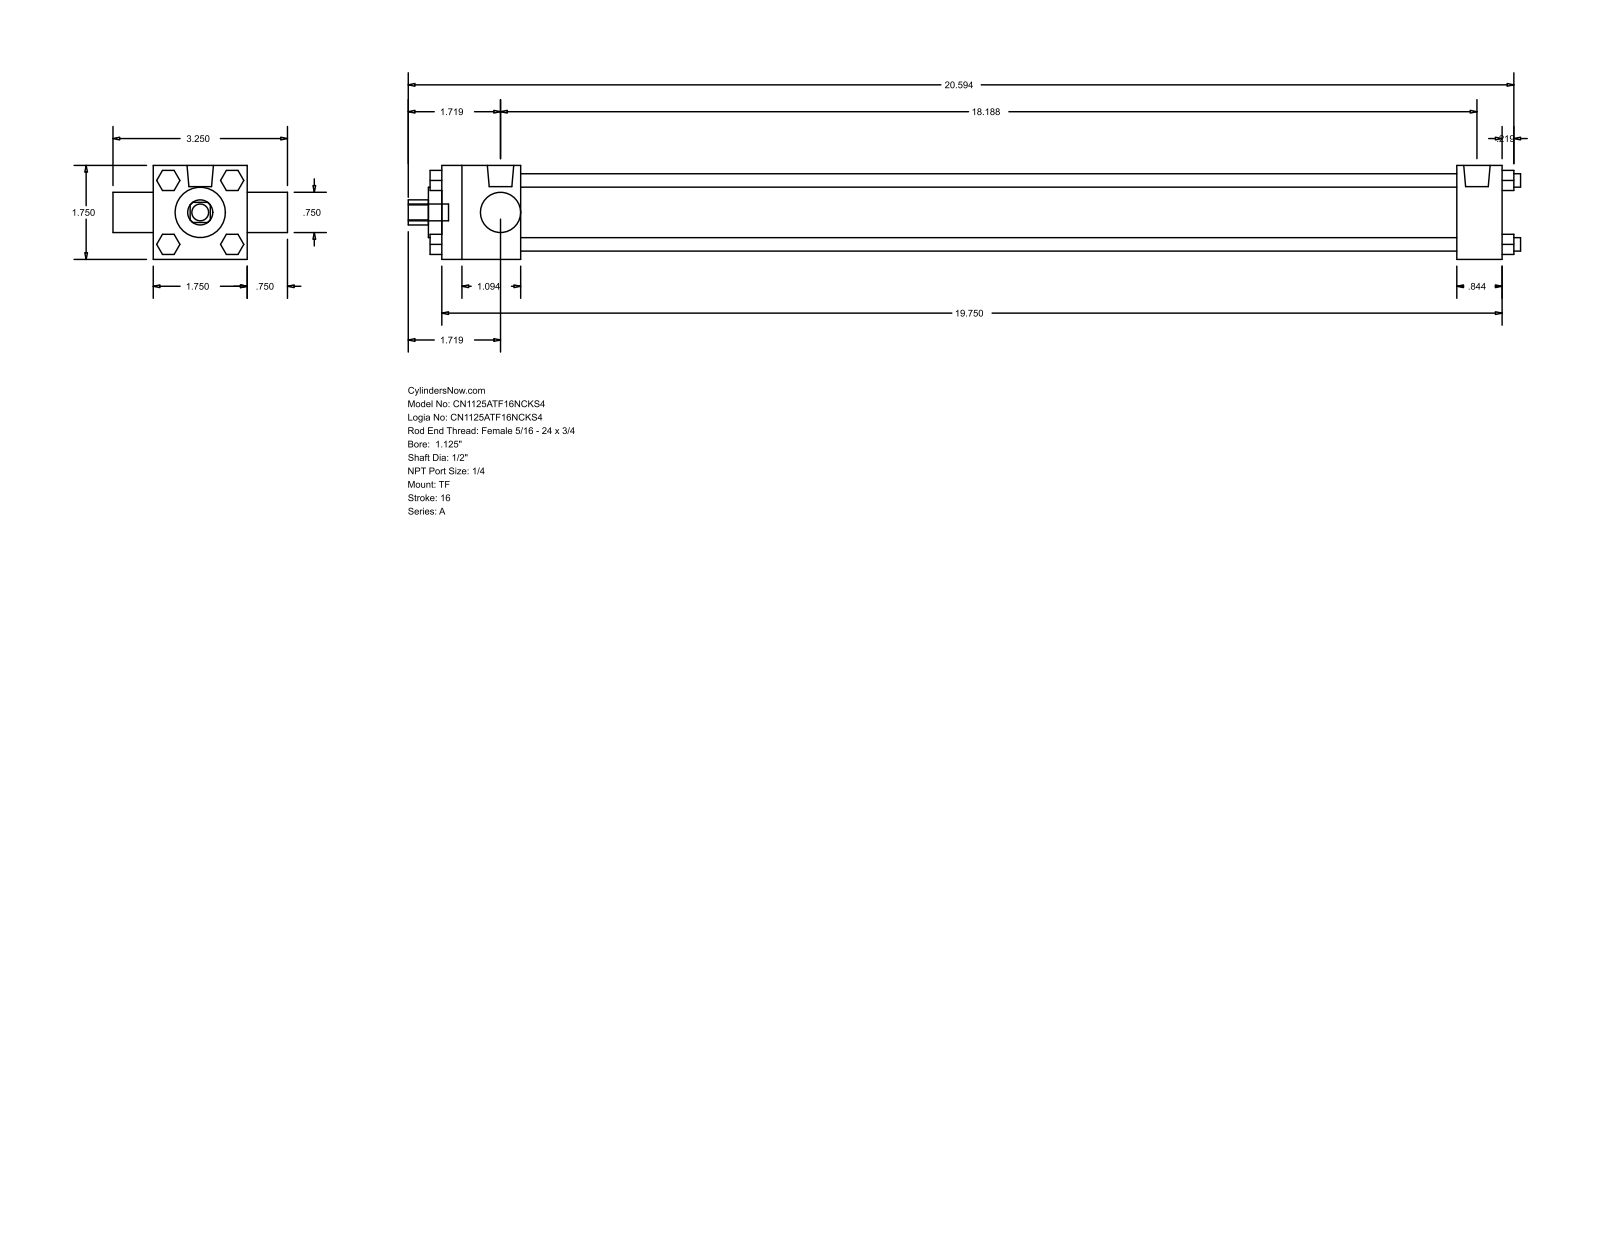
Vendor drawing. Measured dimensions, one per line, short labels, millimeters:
name: A_TF__0112_0.5
written by: GSSL Pune (CONFIG_CONTROL_DESIGN)
unit: mm
bodies: 0 solids, 120 faces (92 planar, 28 cylindrical, 0 other)
size: 526.26 × 82.55 × 44.45
holes: 1× ⌀12.7, 1× ⌀19.05, 1× ⌀23.81, 1× ⌀31.88
bosses: 4× ⌀6.35, 3× ⌀5.56, 2× ⌀12.49, 1× ⌀7.94
rounds: 1× R5.94
face distances: 44.46, 501.64, 480.21, 21.43, 37.3, 442.91, 464.34, 19.04, 63.5, 9.53
